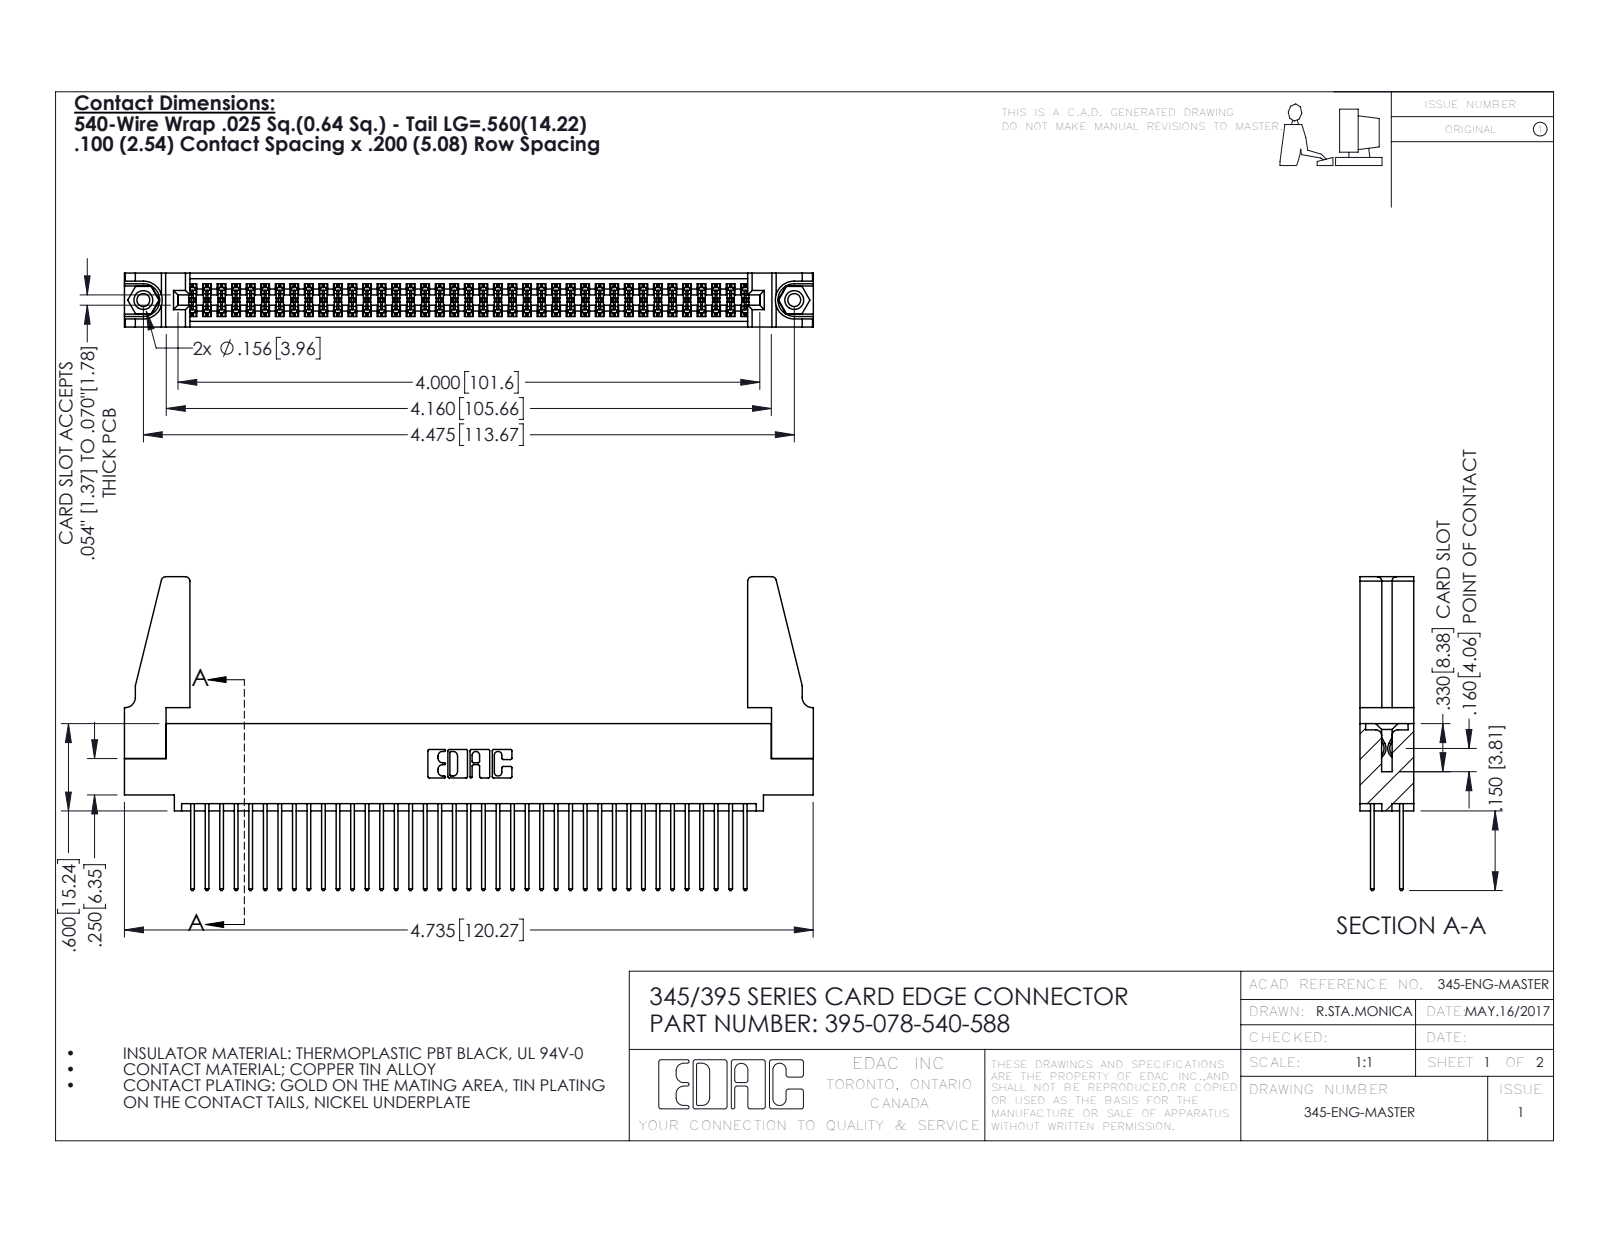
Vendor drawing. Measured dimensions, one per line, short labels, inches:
name: 395-078-540-588; 345 Part_0.110 Offset - 0.156 Dia-TH; 345-220-078_345-220-088; 345-250-001_345-250-001-102 (+1 more)
written by: SolidWorks 2016 (CONFIG_CONTROL_DESIGN)
unit: in
bodies: 83 solids, 4154 faces (2730 planar, 1408 cylindrical, 16 other)
size: 4.736 × 2.157 × 0.37
volume: 0.923 in³; area: 34.24 in²
holes: 2× ⌀0.089, 2× ⌀0.125, 2× ⌀0.156, 1× ⌀0.064
bosses: 2× ⌀0.155
rounds: 117× R0.006, 78× R0.01, 22× R0.01, 8× R0.03, 6× R0.007, 6× R0.031, 3× R0.026, 2× R0.014
face distances: 0.072, 0.298, 0.2, 0.098, 0.272, 0.025, 0.37, 0.225, 0.175, 0.149
hole spacings: 0.27, 4.239, 4.475
